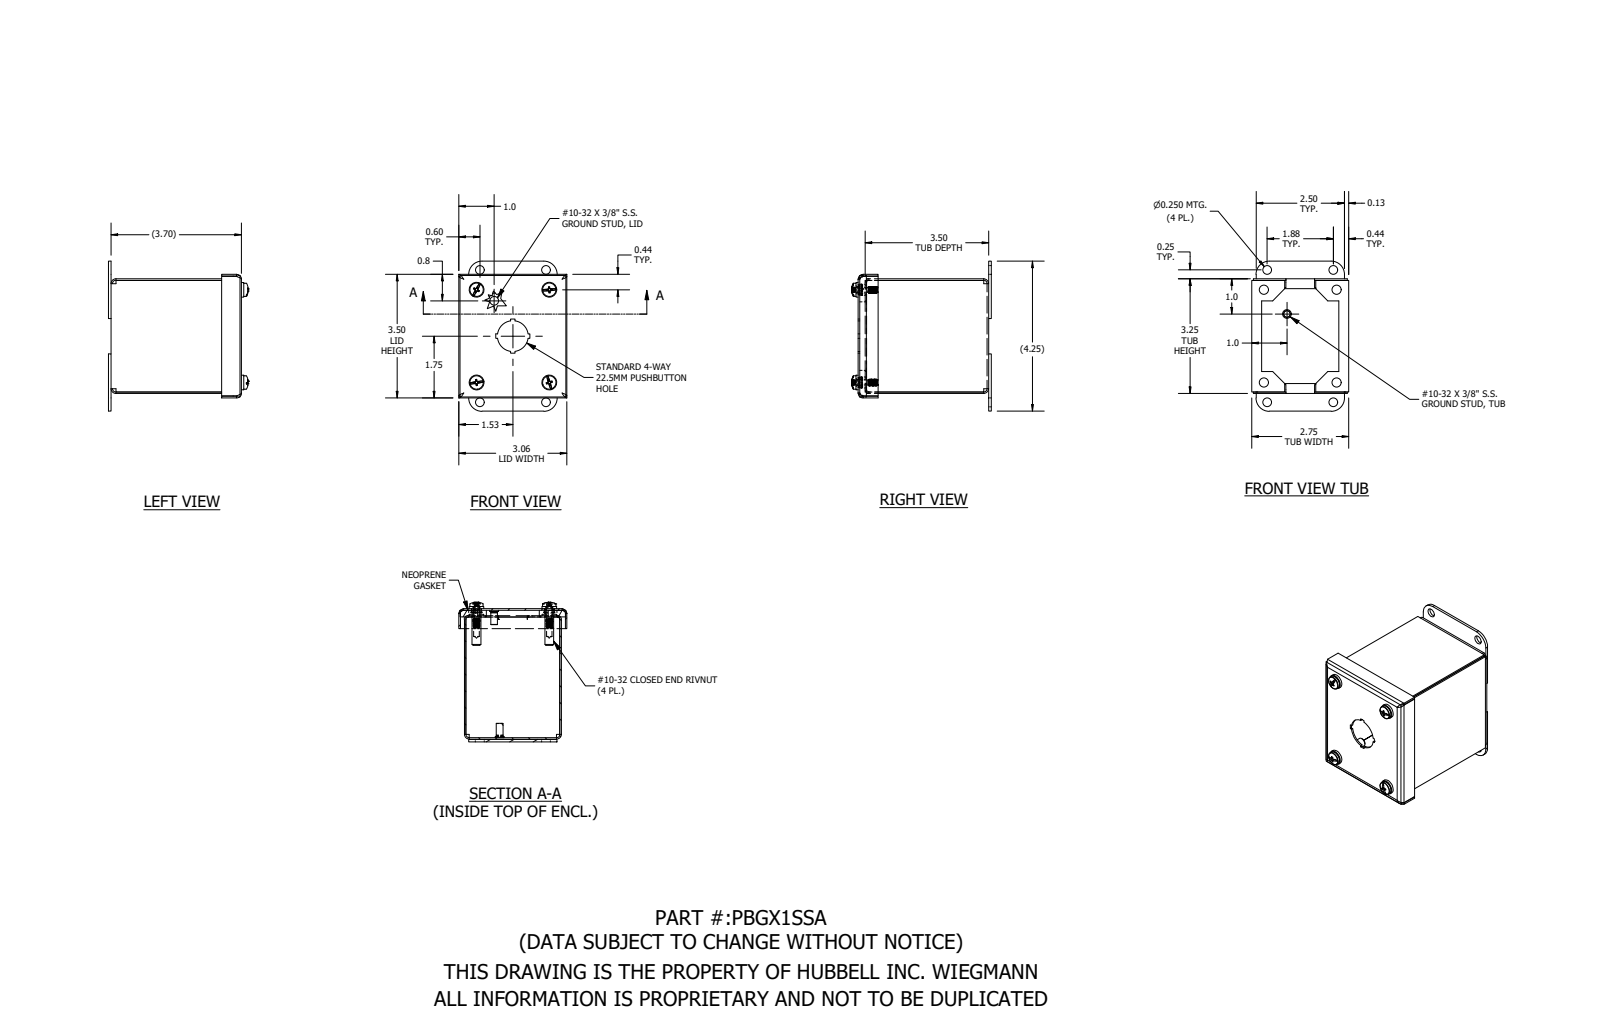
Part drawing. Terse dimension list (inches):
name: PBGX1SSA
written by: SolidWorks 2021 (AUTOMOTIVE_DESIGN)
unit: in
bodies: 19 solids, 718 faces (318 planar, 248 cylindrical, 152 other)
size: 4.25 × 3.954 × 3.063
volume: 4.841 in³; area: 180.1 in²
holes: 4× ⌀0.156, 4× ⌀0.196, 4× ⌀0.25, 4× ⌀0.257, 4× ⌀0.281, 4× ⌀0.313, 2× ⌀0.133, 2× ⌀0.175, 2× ⌀0.175, 1× ⌀0.875
bosses: 4× ⌀0.406, 4× ⌀0.318, 4× ⌀0.248, 4× ⌀0.186, 4× ⌀0.141, 4× ⌀0.14, 3× ⌀0.375, 2× ⌀0.25
rounds: 8× R0.094, 8× R0.139, 4× R0.375, 3× R0.063, 3× R0.108, 1× R0.062, 1× R0.107
face distances: 0.045, 0.045, 3.65, 3.205, 2.75, 2.705, 2.705, 2.66, 3.16, 3.25
hole spacings: 2.626, 3.189, 0.063, 0.063, 0.57, 0.57, 0.583, 0.583
